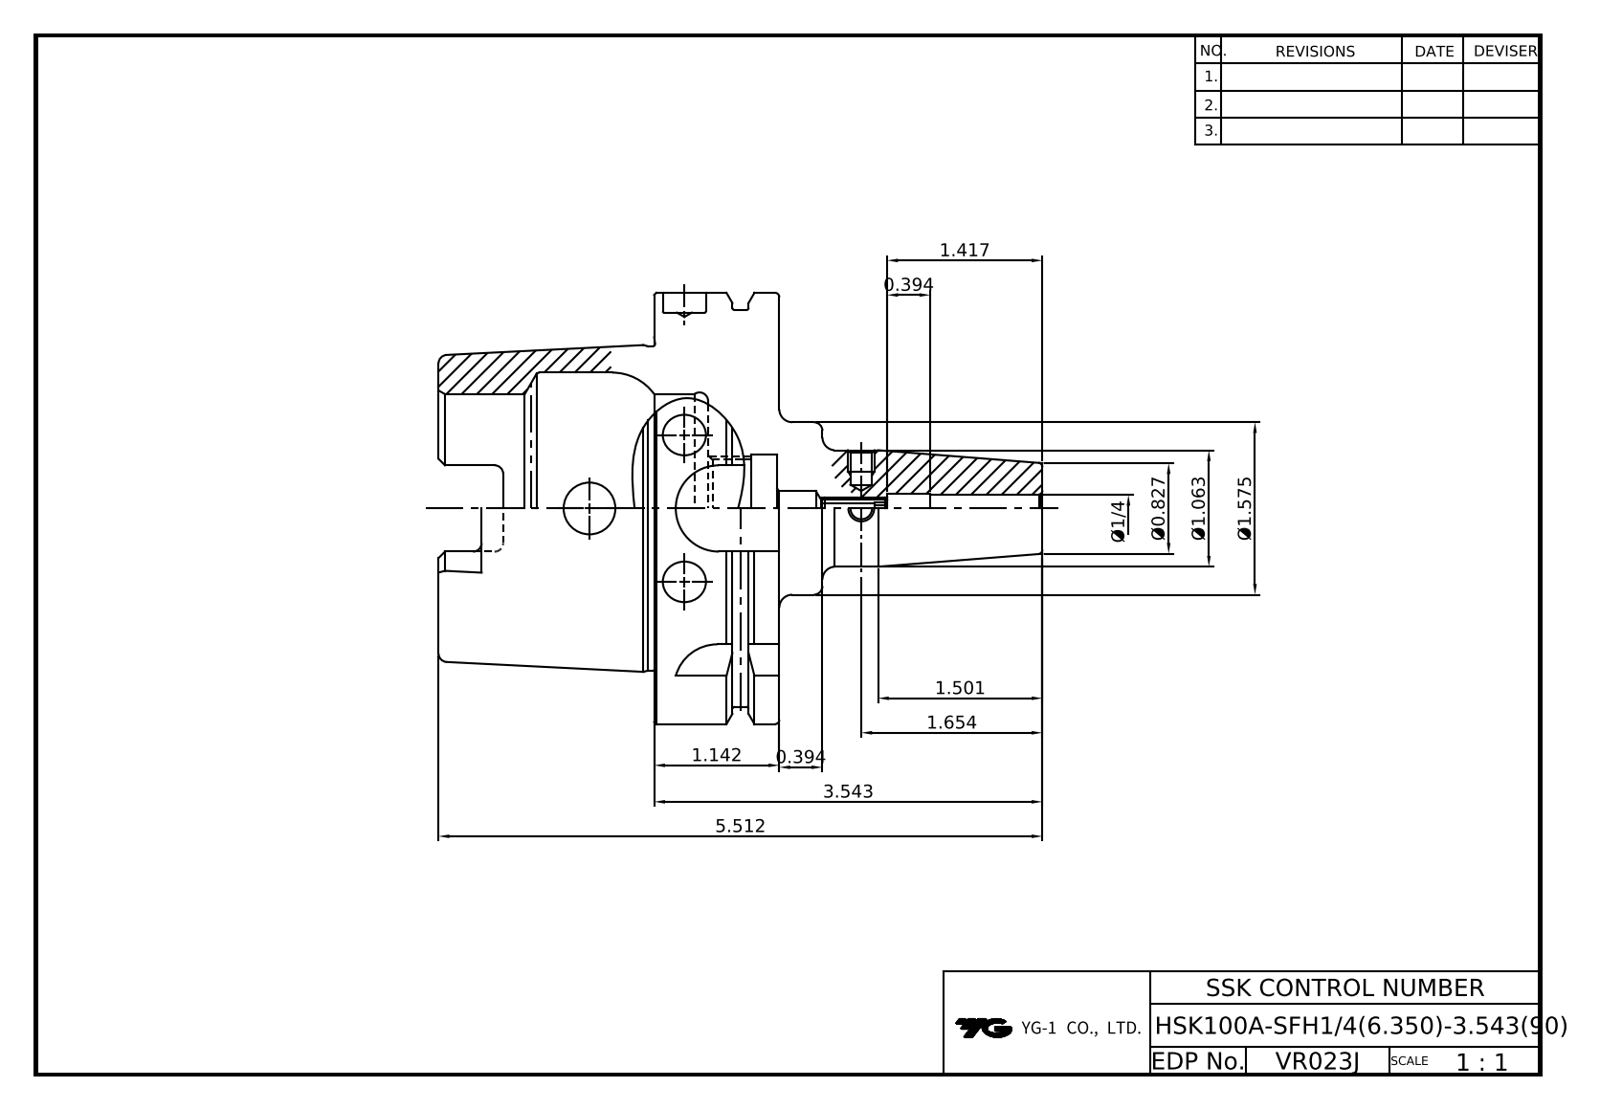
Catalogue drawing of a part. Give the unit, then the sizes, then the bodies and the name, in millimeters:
Units: millimetres
Overall size (bounding box): 140 × 100 × 100
Round holes (diameter × count): ⌀2.5 ×2, ⌀4.3 ×1, ⌀6.35 ×1, ⌀7.55 ×1, ⌀8 ×1, ⌀10 ×1, ⌀12 ×1, ⌀22.38 ×1, ⌀25 ×1, ⌀53 ×1, ⌀63 ×1
Round bosses / shafts (diameter × count): ⌀100 ×1, ⌀92 ×1, ⌀75.41 ×1, ⌀40 ×1, ⌀27 ×1
Partial cylindrical surfaces — rounded edges, fillets, slot ends (radius × count): R2 ×6, R4.88 ×4, R10 ×4
Main face-to-face distances: 29, 12.5, 16.5, 79, 62.5, 50, 68.12, 71.88, 10, 78.5
Volume: 289 337 mm³ · Surface area: 56 061 mm²
Bodies: 1 solid, 123 faces (39 planar, 38 cylindrical, 46 other)
Part name (STEP PRODUCT): LO-HSK100A-SFH6.35C-90
STEP written by: Autodesk Inventor 2022 (AUTOMOTIVE_DESIGN)
